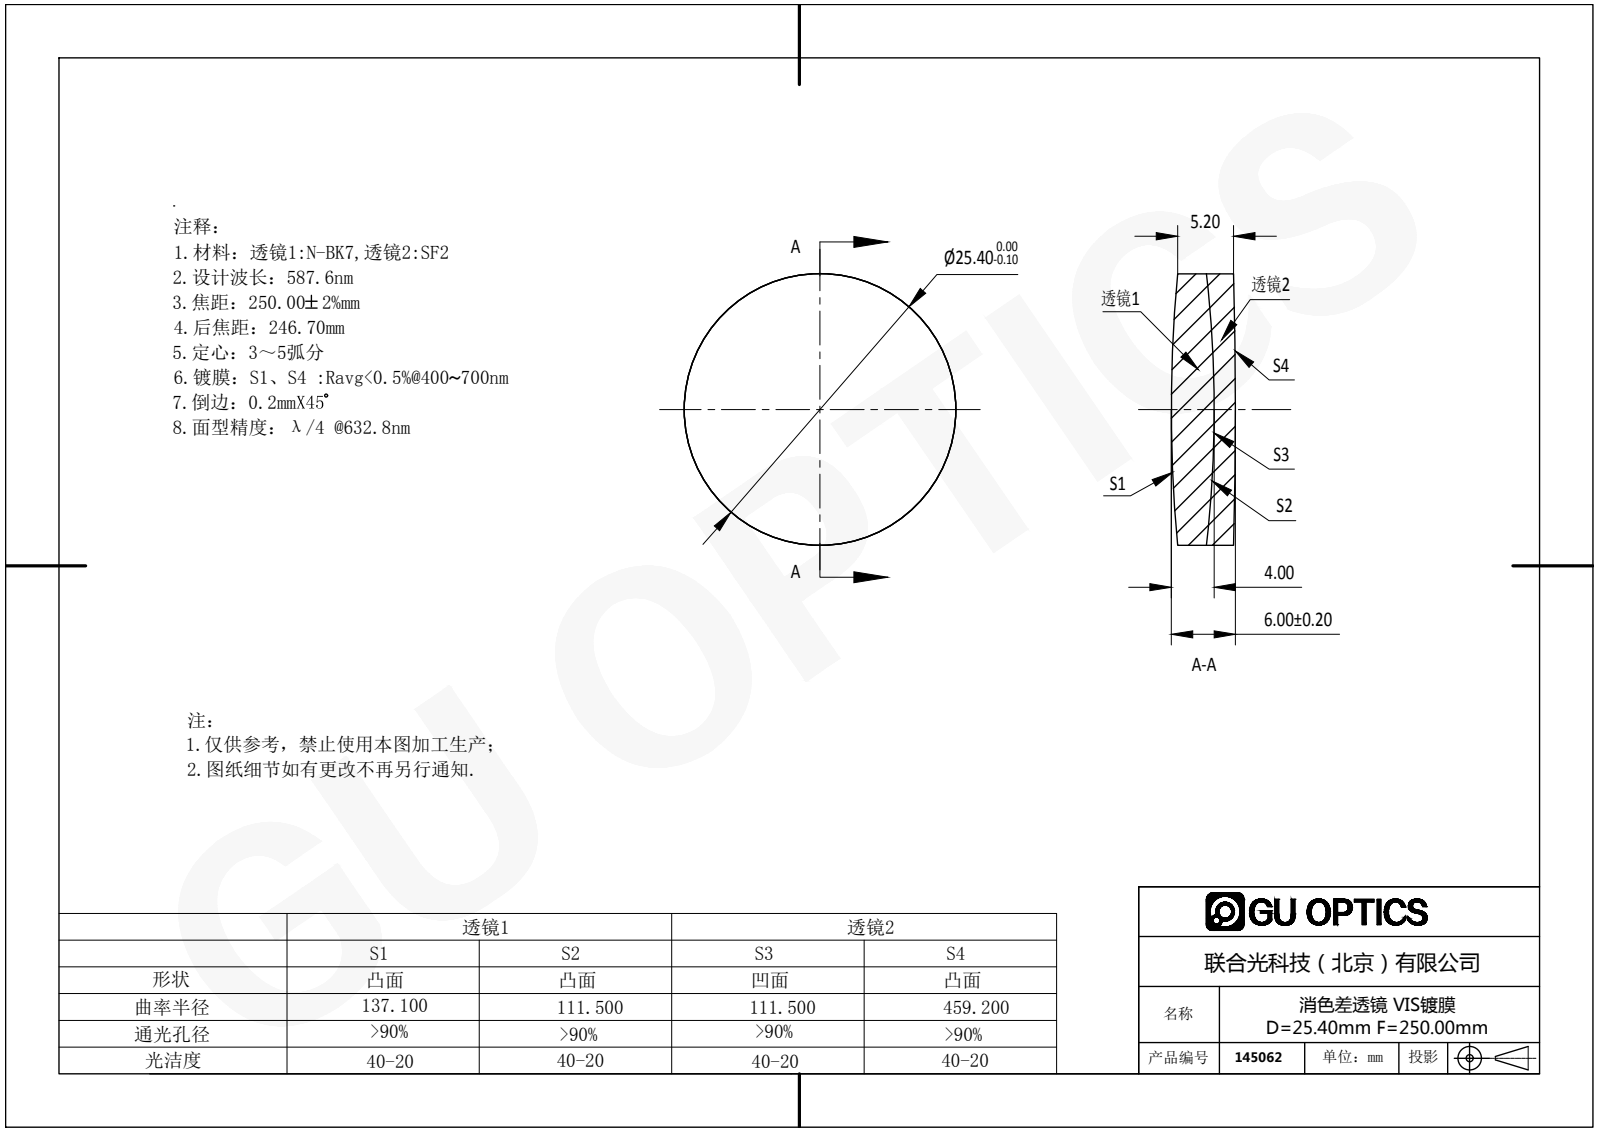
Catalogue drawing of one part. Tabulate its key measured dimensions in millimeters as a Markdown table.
| quantity | value |
| --- | --- |
| part name | 145062 |
| STEP written by | SolidWorks 2016 (AUTOMOTIVE_DESIGN) |
| units | millimeters |
| bodies | 2 solids, 12 faces (0 planar, 4 cylindrical, 8 other) |
| overall size | 25.4 × 25.4 × 6 |
| volume | 2 847 mm³ |
| surface area | 2 449 mm² |
| round bosses / shafts (diameter × count) | 25.4 × 1 |
